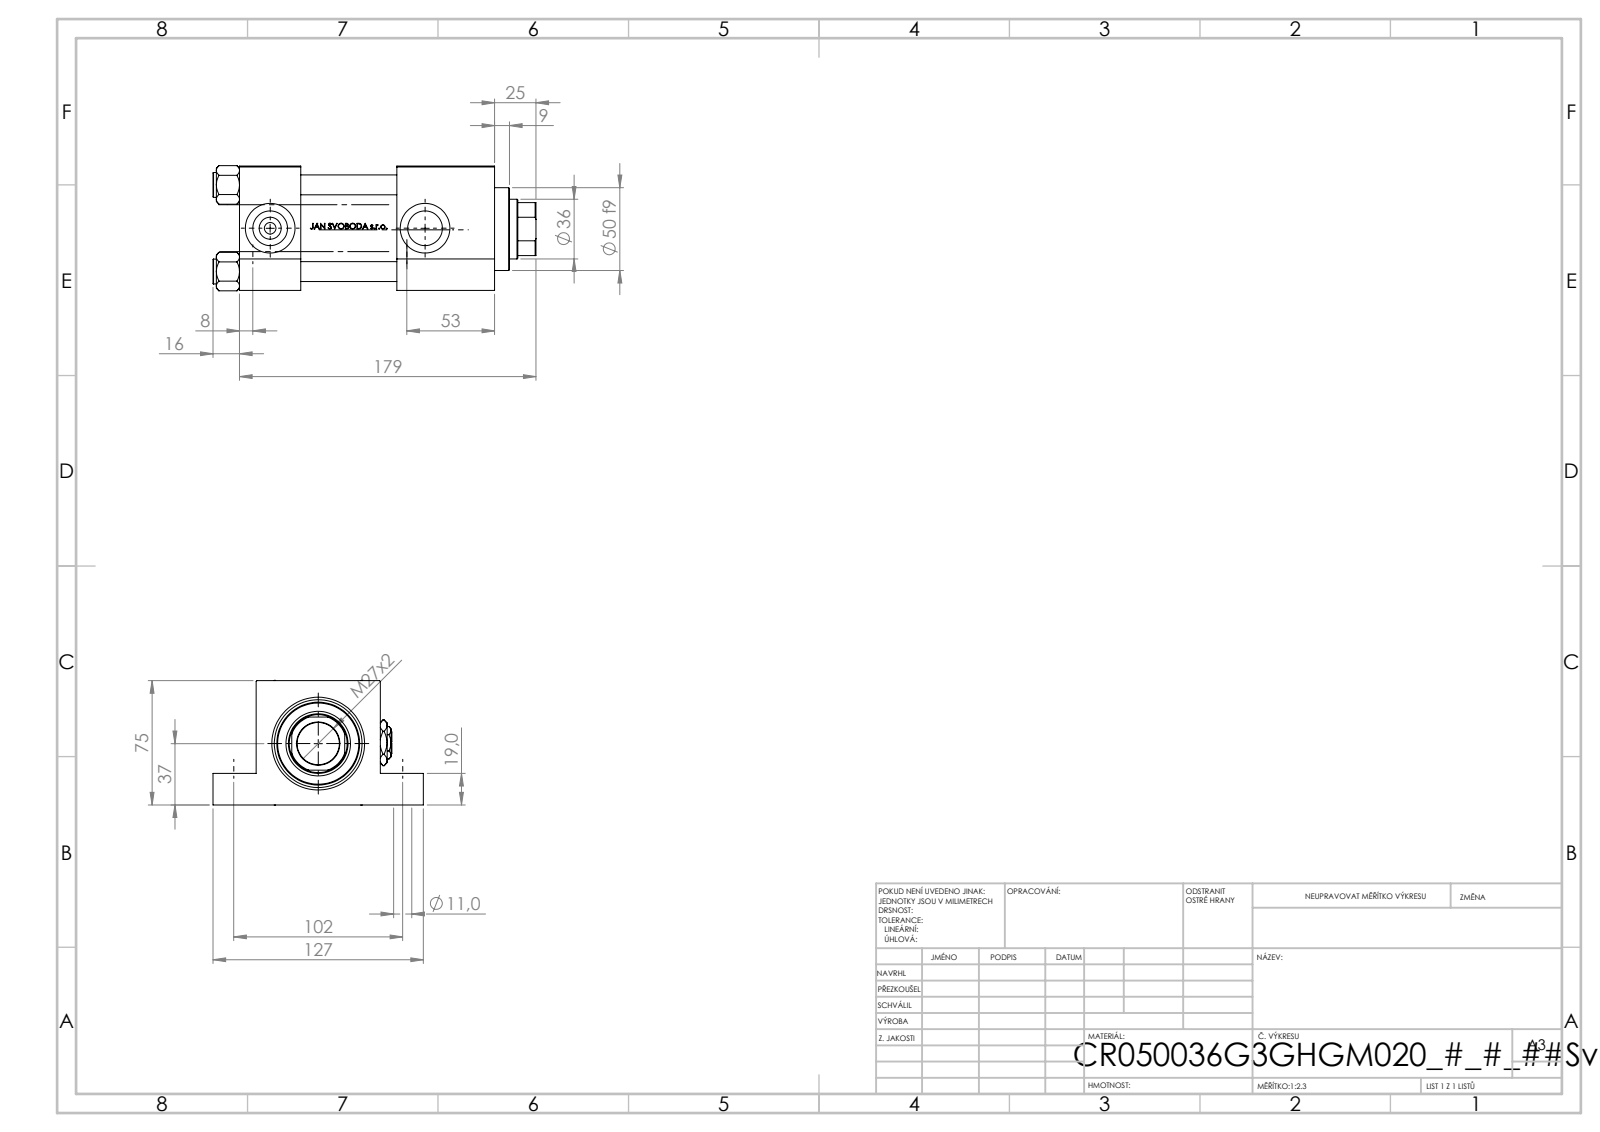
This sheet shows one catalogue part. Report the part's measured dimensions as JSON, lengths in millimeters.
{"part_name": "V215_VC_A; Zatka_pro_OIL_PORT; V215CR_G_TYCINKA; NUT_M5_G (+2 more)", "step_written_by": "SolidWorks 2019 (CONFIG_CONTROL_DESIGN)", "units": "millimeters", "bodies": {"solids": 13, "faces": 1183, "planar": 477, "cylindrical": 132, "other": 574}, "overall_size": [195, 127, 75.54], "volume_mm3": 779302, "surface_area_mm2": 172121, "round_holes": [[12, 4], [11, 3], [7, 2], [20.96, 2], [30, 2], [11, 1], [25.5, 1], [36, 1], [39, 1], [41, 1], [53, 1]], "round_bosses_or_shafts": [[15, 4], [56, 1], [50, 1]], "partial_cylinders_radius": [[17.5, 1]], "face_to_face_distances": [75, 37, 19, 56, 154, 117, 95, 59, 58, 26], "hole_center_spacings": [52.3, 36.63, 37.34, 73.96, 102, 112, 151.49, 93.5]}
